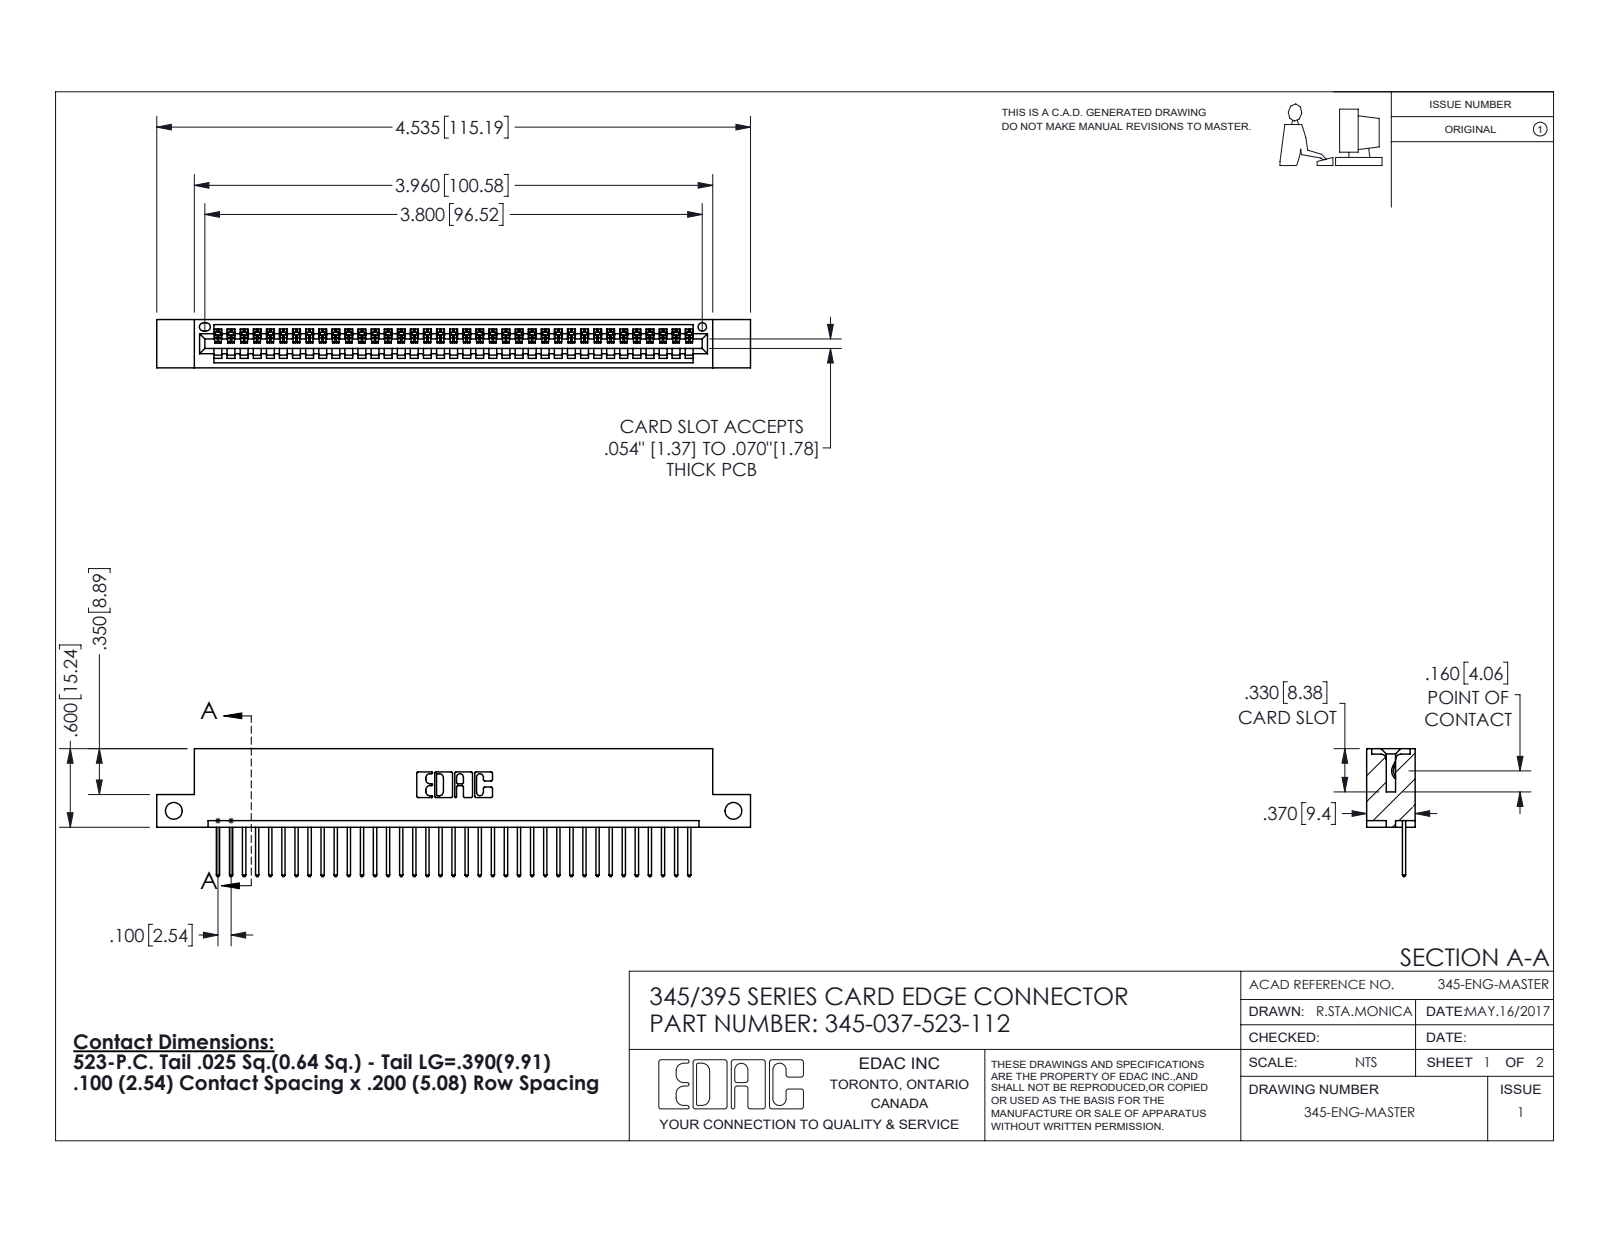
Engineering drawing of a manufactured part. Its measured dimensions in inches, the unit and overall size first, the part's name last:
Units: inches
Overall size (bounding box): 4.535 × 0.977 × 0.37
Round holes (diameter × count): ⌀0.128 ×2, ⌀0.064 ×1
Partial cylindrical surfaces — rounded edges, fillets, slot ends (radius × count): R0.006 ×74, R0.01 ×74, R0.01 ×22, R0.007 ×6, R0.031 ×6, R0.026 ×3, R0.031 ×2, R0.04 ×2
Main face-to-face distances: 0.298, 0.072, 0.2, 0.37, 0.098, 0.272, 0.025, 0.225, 0.149, 0.072
Hole centre spacings: 4.275
Volume: 0.659 in³ · Surface area: 21.98 in²
Bodies: 38 solids, 2272 faces (1560 planar, 712 cylindrical, 0 other)
Part name (STEP PRODUCT): 345-292-001_345-293-123; 345-037-523-112; 345 Part_Flush Mounting Lugs - Side Mount
STEP written by: SolidWorks 2016 (CONFIG_CONTROL_DESIGN)
